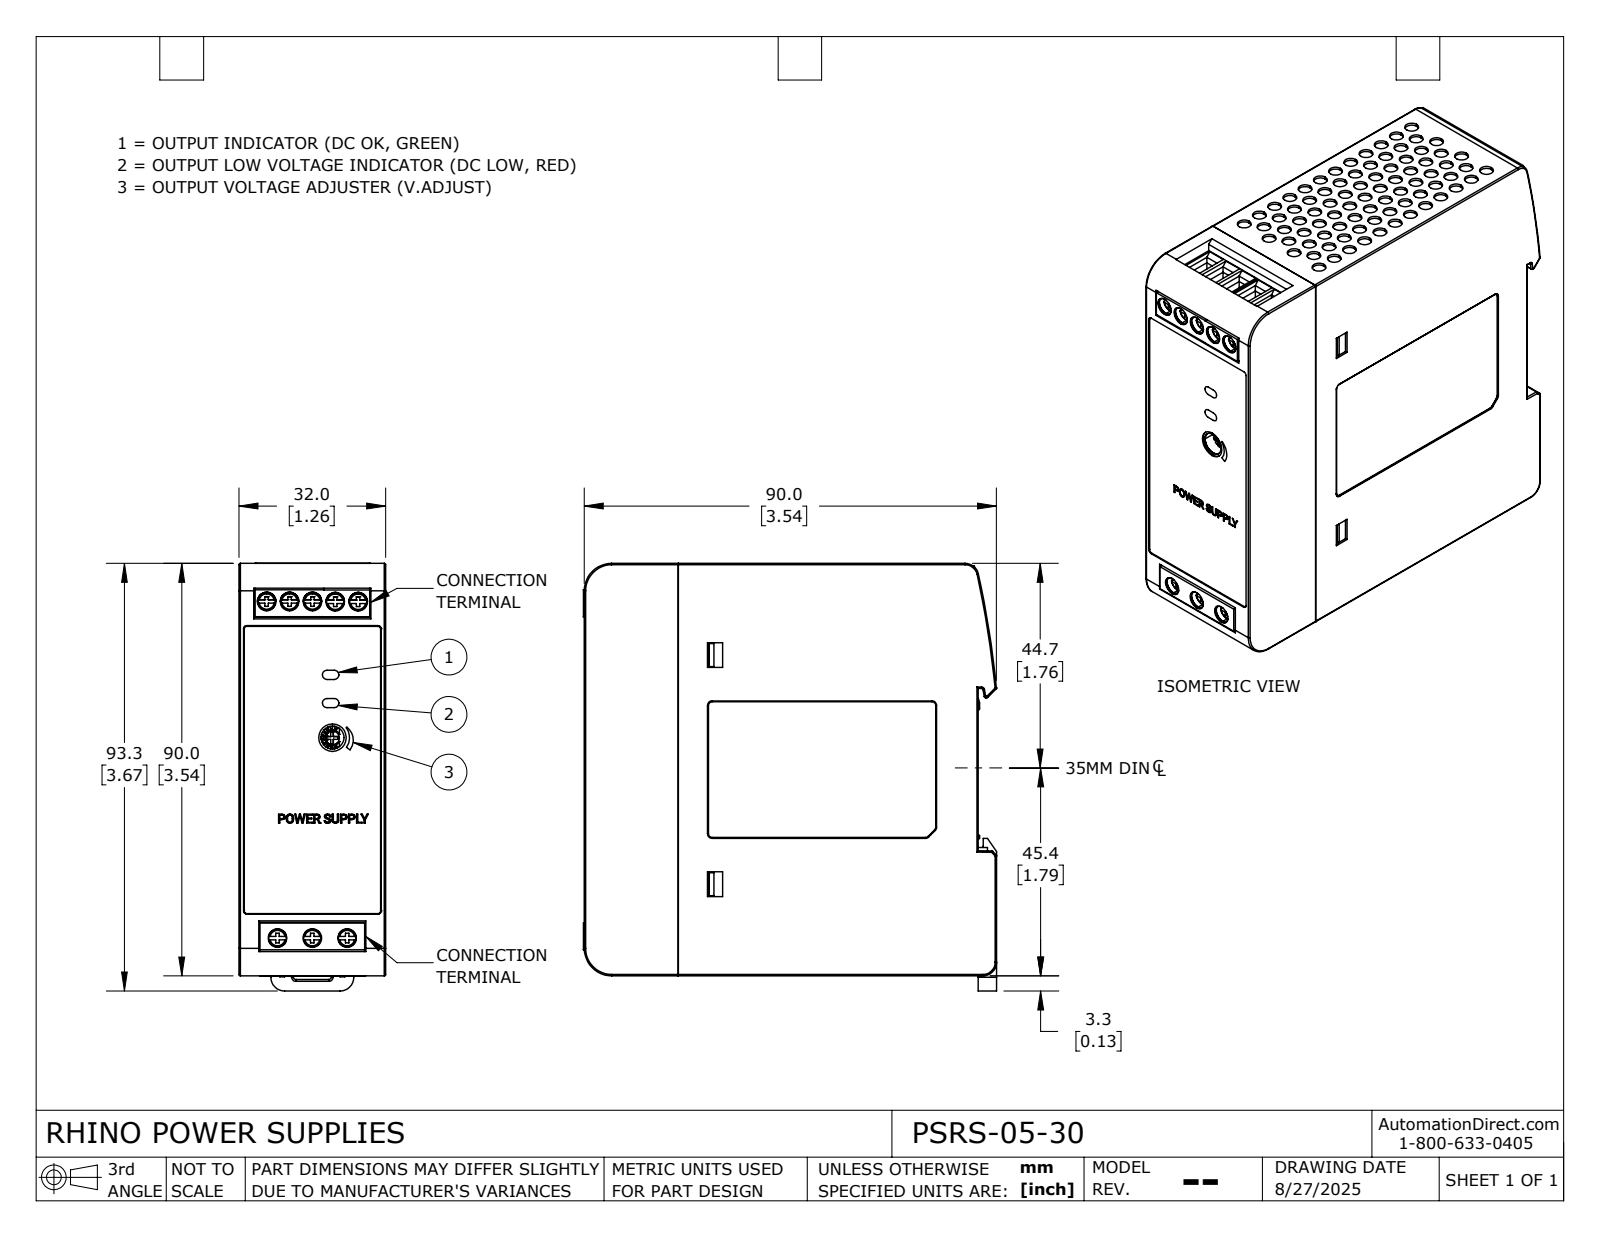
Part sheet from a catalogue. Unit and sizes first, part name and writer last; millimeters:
Units: millimetres
Overall size (bounding box): 93.3 × 90.2 × 32
Round holes (diameter × count): ⌀3.82 ×8, ⌀4.05 ×8, ⌀3.4 ×1, ⌀5 ×1
Round bosses / shafts (diameter × count): ⌀3.95 ×8, ⌀3 ×1
Partial cylindrical surfaces — rounded edges, fillets, slot ends (radius × count): R0.3 ×49, R1 ×12, R0.5 ×7, R0.1 ×6, R3 ×4, R2.5 ×3, R0.6 ×2, R5.5 ×2
Main face-to-face distances: 32, 90, 31.85, 85.85, 0.5, 89.5, 4, 89.85, 89, 2
Hole centre spacings: 5, 7.6, 9.97, 14.97, 43.87, 73.43, 4.97, 10
Volume: 248 207 mm³ · Surface area: 32 836 mm²
Bodies: 1 solid, 1376 faces (733 planar, 191 cylindrical, 452 other)
Part name (STEP PRODUCT): PSRS-05-30
STEP written by: SolidWorks 2024 (AUTOMOTIVE_DESIGN)
